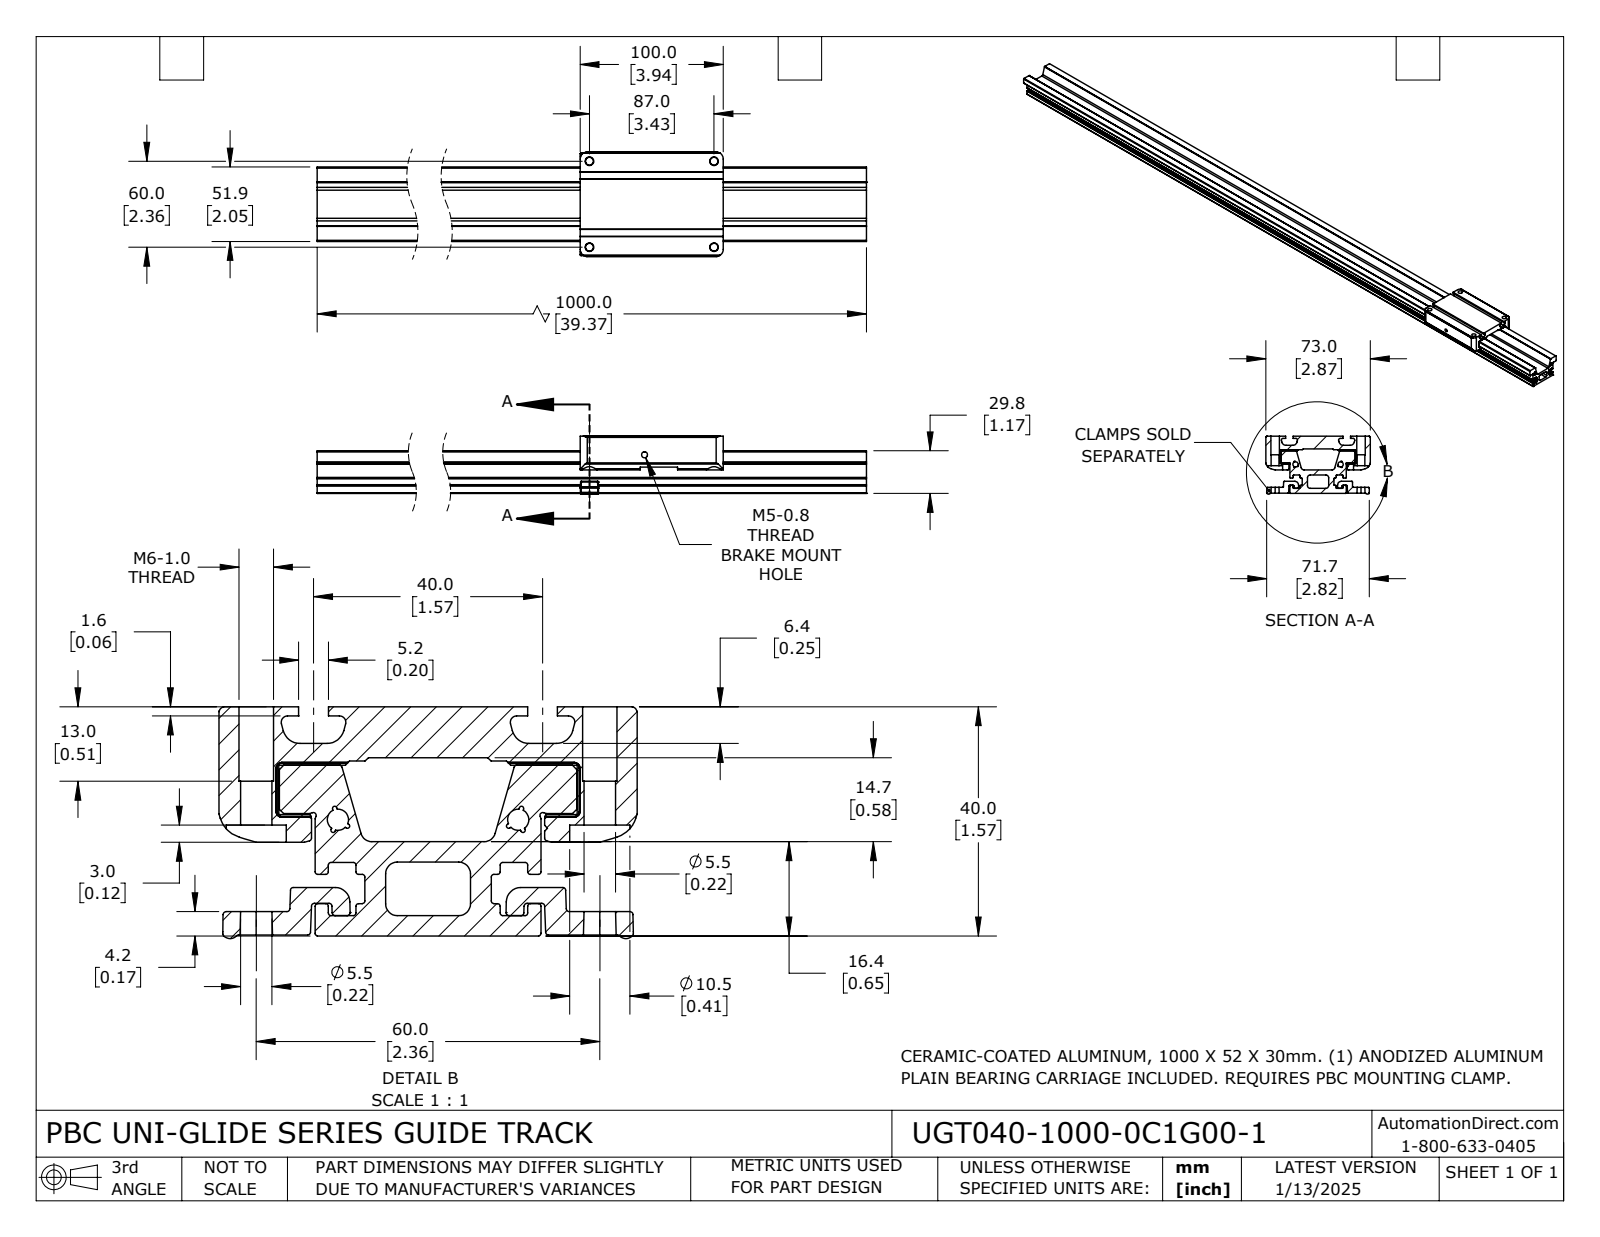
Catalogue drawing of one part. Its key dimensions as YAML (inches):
part_name: "UGT040-1000-0C1G00-1; UGT040-1000-0C1G00-1_RAIL; UGT040-1000-0C1G00-1_CARRIAGE"
step_written_by: "SolidWorks 2023 (CONFIG_CONTROL_DESIGN)"
units: inches
bodies: {solids: 10, faces: 445, planar: 248, cylindrical: 178, other: 19}
overall_size: [39.37, 2.874, 1.575]
volume: 44.14
surface_area: 538.6
round_holes:
  - {diameter: 0.098, count: 4}
  - {diameter: 0.118, count: 4}
  - {diameter: 0.217, count: 4}
  - {diameter: 0.236, count: 4}
  - {diameter: 0.413, count: 4}
  - {diameter: 0.146, count: 2}
  - {diameter: 0.165, count: 1}
partial_cylinders:
  - {radius: 0.019, count: 26}
  - {radius: 0.039, count: 8}
  - {radius: 0.094, count: 8}
  - {radius: 0.015, count: 6}
  - {radius: 0.197, count: 6}
  - {radius: 0.02, count: 4}
  - {radius: 0.035, count: 4}
  - {radius: 0.043, count: 4}
face_to_face_distances: [0.14, 0.507, 1.173, 0.648, 0.526, 1.033, 1.553, 0.246, 1.799, 0.367]
hole_center_spacings: [0.591, 1.221, 1.615, 1.811, 2.205, 2.283, 2.359, 2.362]
